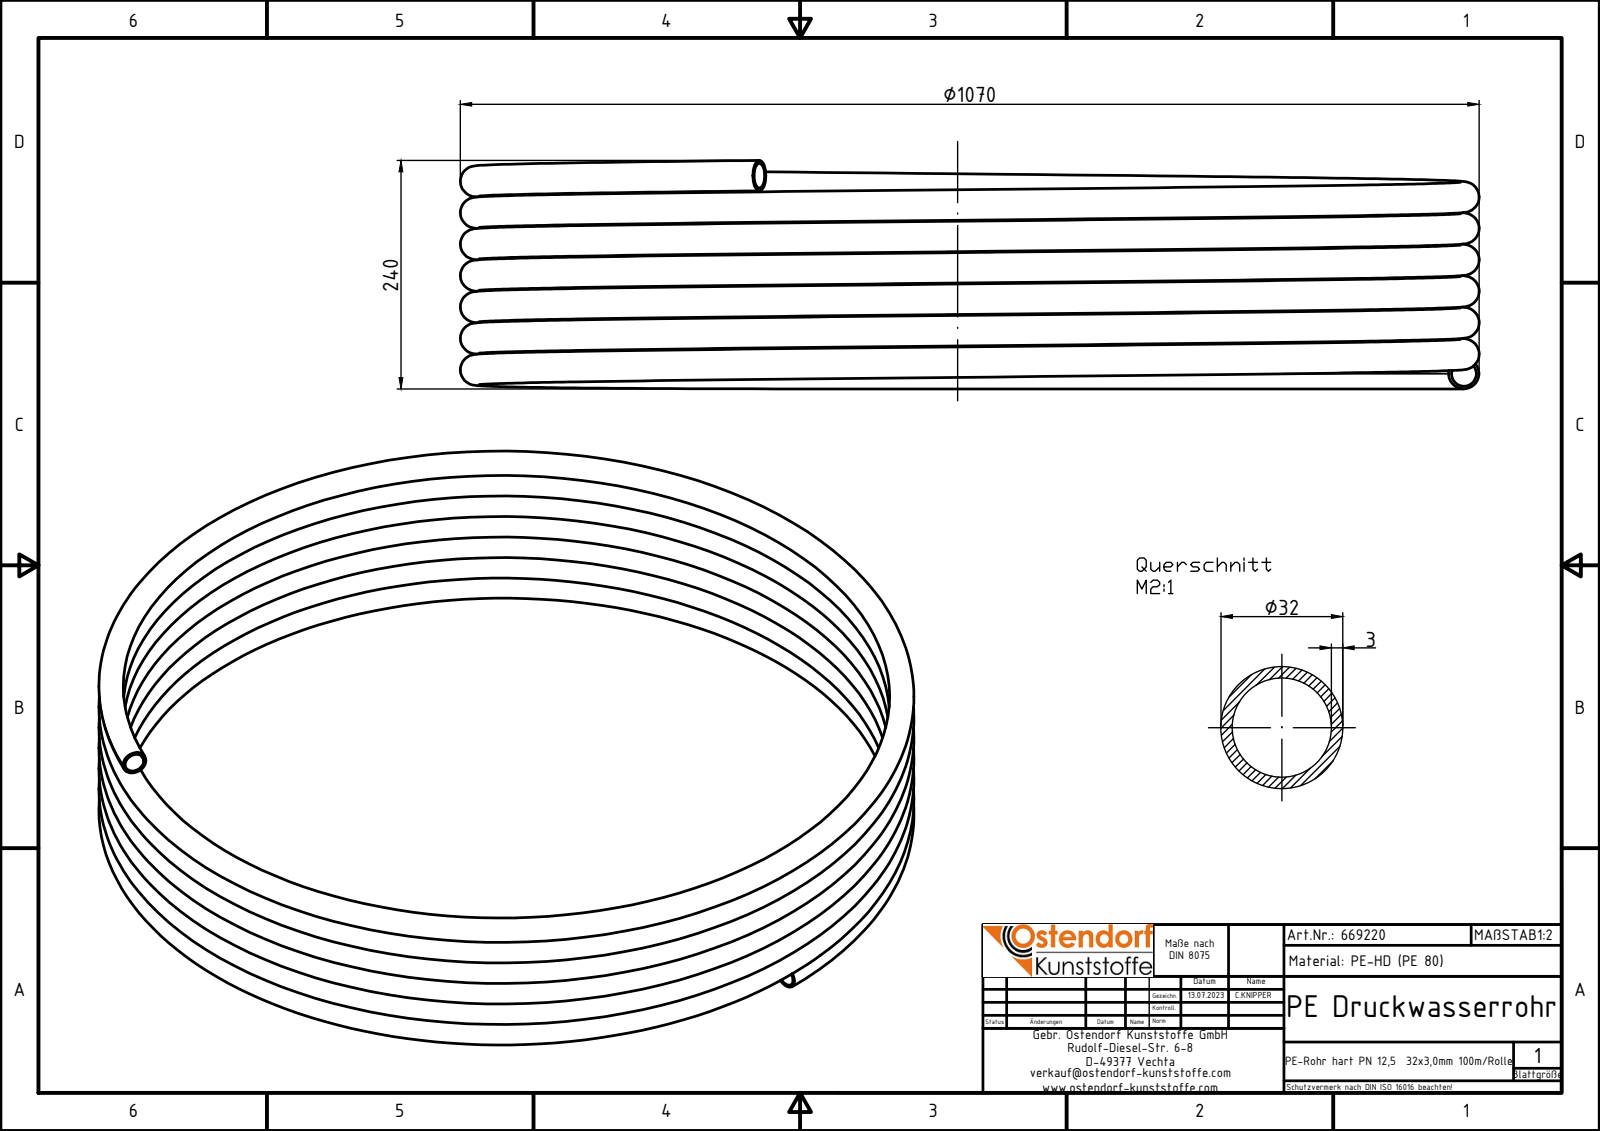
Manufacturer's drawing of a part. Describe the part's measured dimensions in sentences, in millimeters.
The part is named "669220z". Its 3-D file was written by "Autodesk Inventor 2024 (AUTOMOTIVE_DESIGN)". It is 1 solid with 7 faces: 3 planar, 0 cylindrical and 4 other. Overall it measures 1070.01 by 1070 by 240.06 millimeters. Its volume is 5 709 000 cubic millimeters and its surface area 3 916 000 square millimeters.
